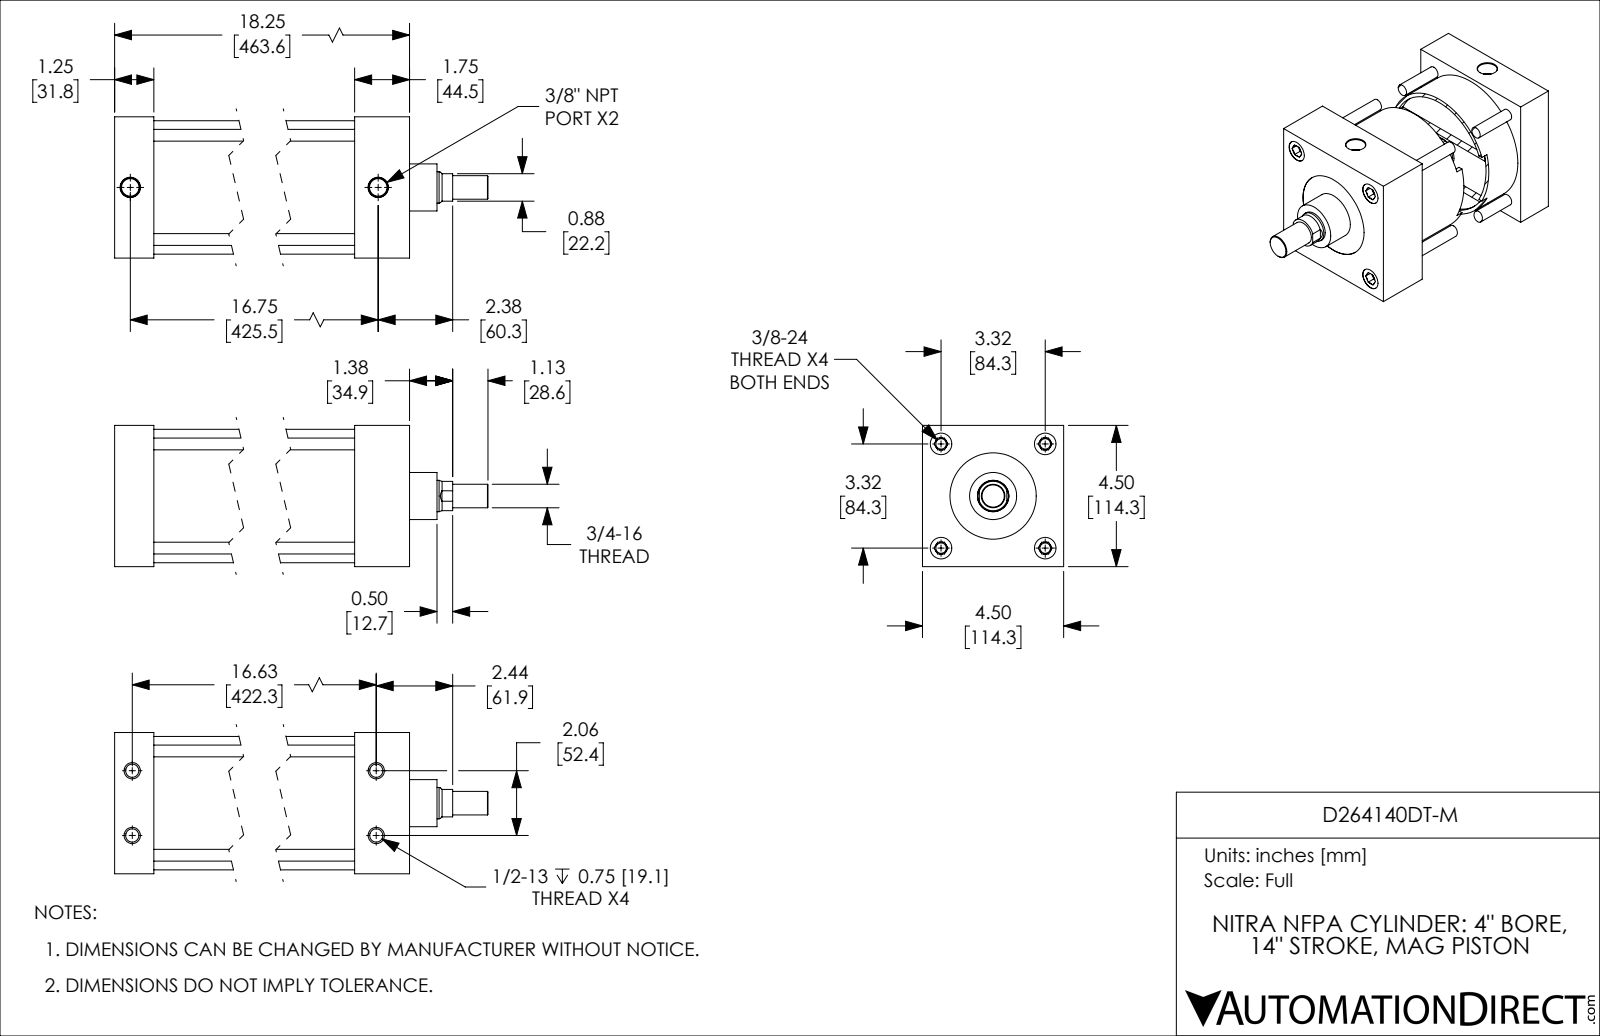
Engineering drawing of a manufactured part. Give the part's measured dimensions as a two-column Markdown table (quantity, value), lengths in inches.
| quantity | value |
| --- | --- |
| part name | D264140DT-M_BODY; D264140DT-M; D264140DT-M_PISTON_KK1 |
| STEP written by | SolidWorks 2019 (CONFIG_CONTROL_DESIGN) |
| units | inches |
| bodies | 2 solids, 198 faces (58 planar, 62 cylindrical, 78 other) |
| overall size | 20.75 × 4.5 × 4.5 |
| volume | 118.9 in³ |
| surface area | 725.9 in² |
| round holes (diameter × count) | 0.332 × 4, 0.422 × 4, 0.687 × 4, 0.562 × 2, 1.001 × 1, 2.75 × 1, 4.001 × 1 |
| round bosses / shafts (diameter × count) | 0.375 × 4, 4.251 × 1, 3.999 × 1, 1.5 × 1, 0.999 × 1, 0.75 × 1 |
| partial cylindrical surfaces (radius × count) | 0.469 × 1 |
| main face-to-face distances | 1.25, 4.5, 16.5, 15.25, 18.25, 17, 1.75, 2.5, 14, 15.75 |
| hole center spacings | 2.347, 3.32, 16.719, 1.033, 4.695, 16.625, 16.752, 1.034 |
